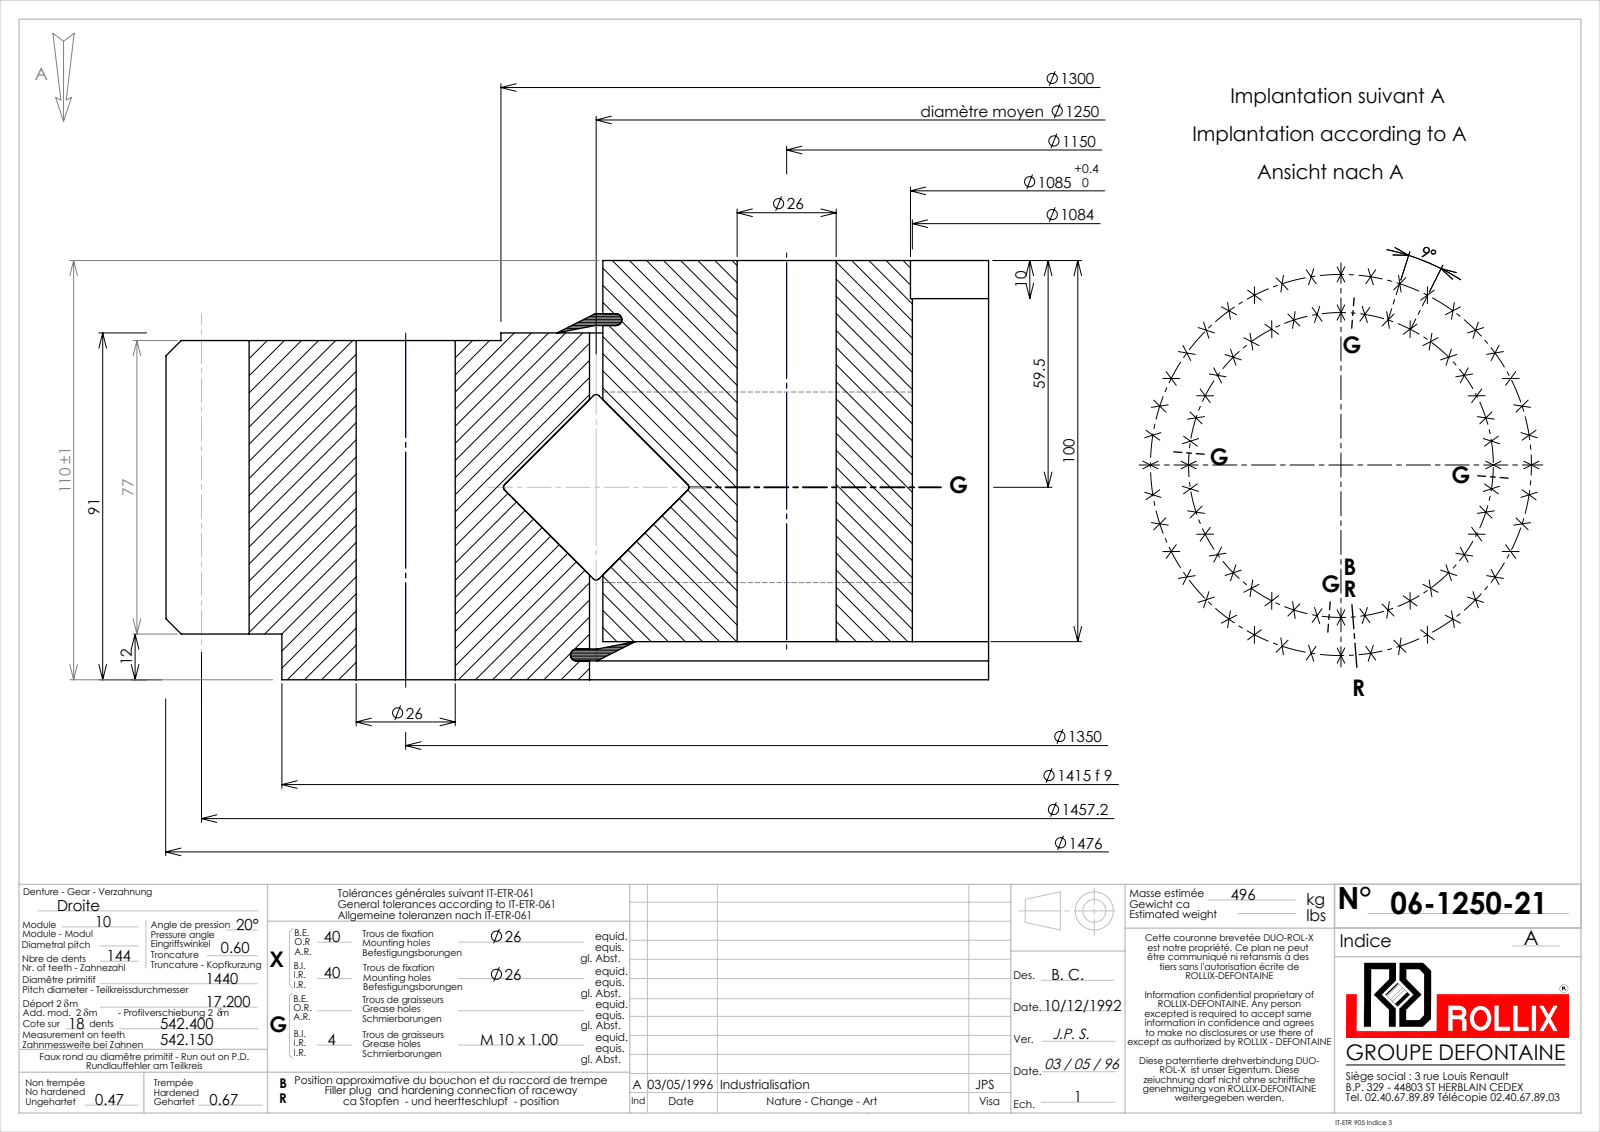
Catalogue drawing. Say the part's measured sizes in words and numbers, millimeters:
The part is named "06-1250-21". Its 3-D file was written by "SolidWorks 2016 (CONFIG_CONTROL_DESIGN)". It is 5 solids with 1124 faces: 305 planar, 479 cylindrical and 340 other. Overall it measures 1475.83 by 1475.83 by 110 millimeters. Its volume is 59 110 000 cubic millimeters and its surface area 4 344 000 square millimeters. Round holes: 80 of diameter 26, 4 of diameter 9, 1 of diameter 1084, 1 of diameter 1085, 1 of diameter 1253.5. Round bosses or shafts: 1 of diameter 1415, 1 of diameter 1300, 1 of diameter 1246.5, 1 of diameter 35. Partial cylindrical surfaces (rounded edges, fillets, slot ends): 1 of radius 716.1, 1 of radius 738. The main face-to-face distances are 79, 89, 10, 100, 110, 21, 2, 91, 81, 19. The hole center spacings are 315.15, 1312.7, 516.62, 612.89, 1333.38, 211.19, 793.51, 417.18.
